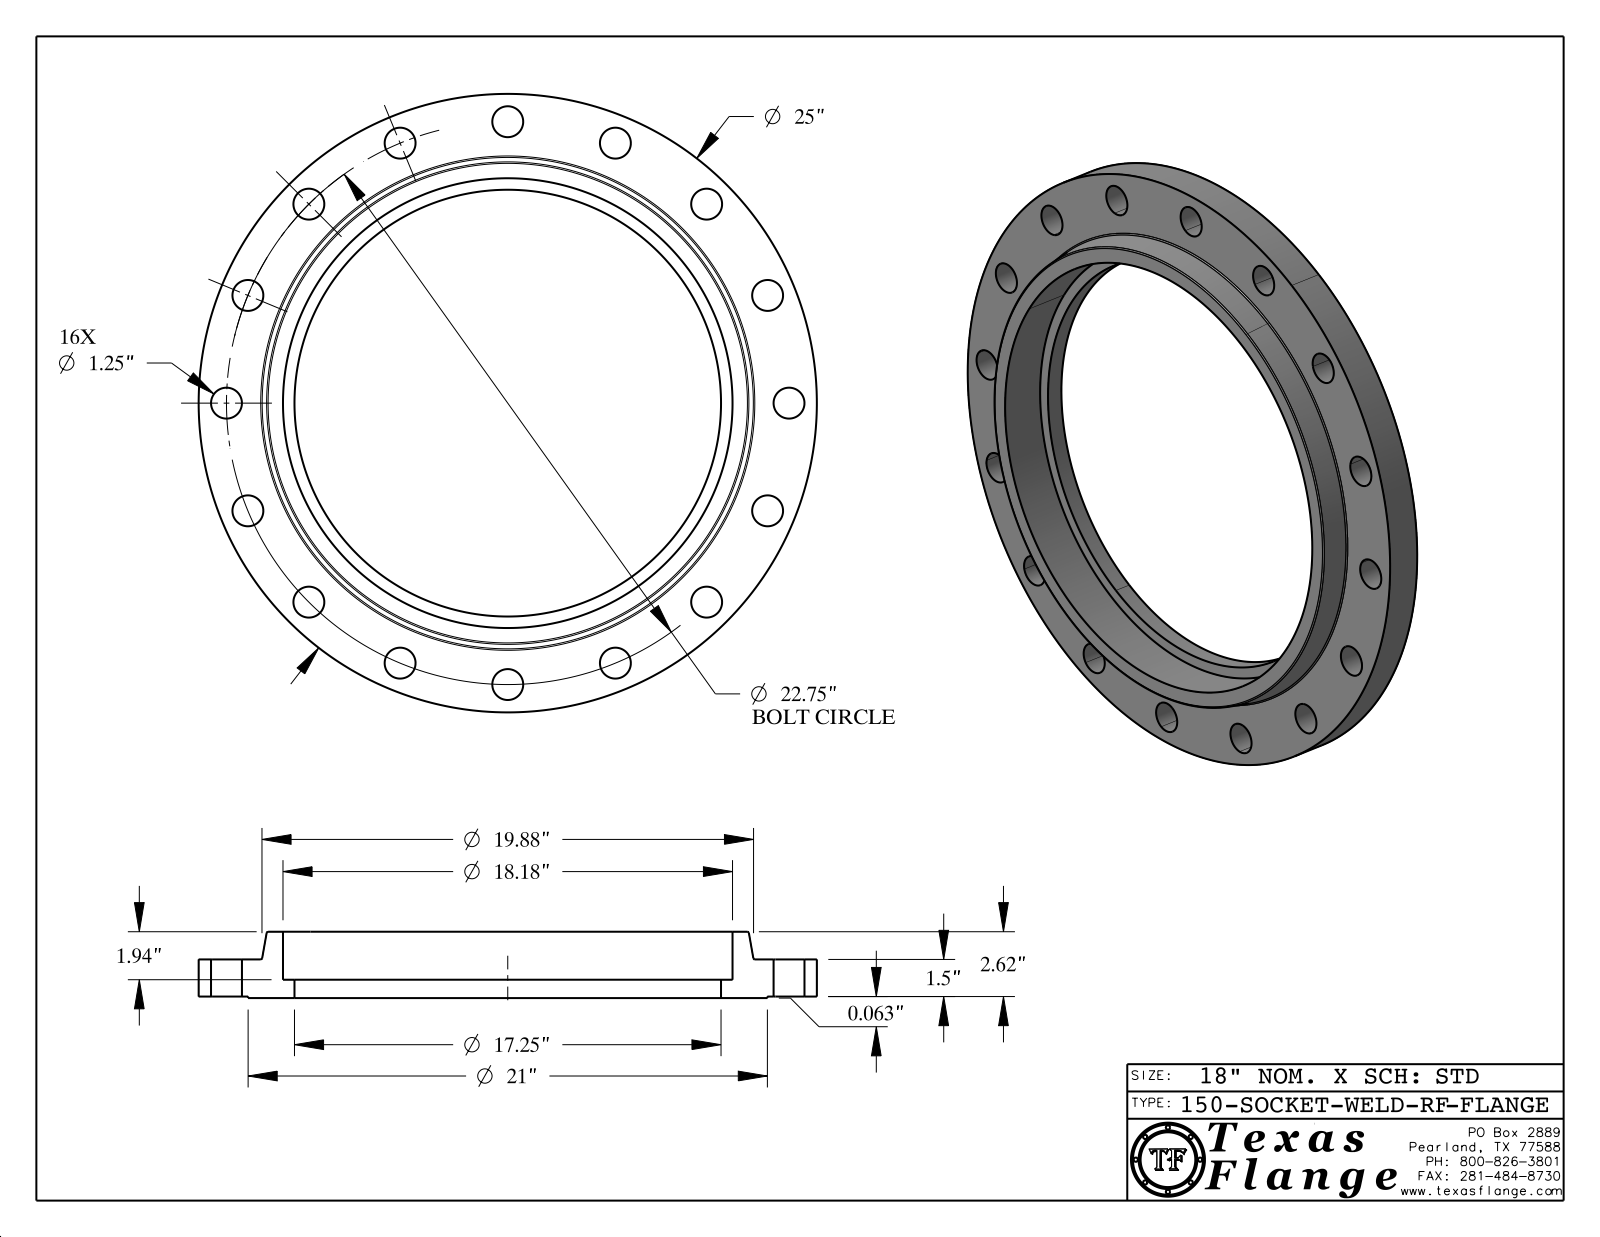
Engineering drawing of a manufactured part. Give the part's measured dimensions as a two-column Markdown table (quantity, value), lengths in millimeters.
| quantity | value |
| --- | --- |
| part name | 150-SOCKET-WELD-RF |
| STEP written by | CATIA V5 STEP AP214 (AUTOMOTIVE_DESIGN) |
| units | millimeters |
| bodies | 1 solid, 436 faces (370 planar, 60 cylindrical, 6 other) |
| overall size | 635 × 635 × 68.1 |
| volume | 6 427 000 mm³ |
| surface area | 579 600 mm² |
| round holes (diameter × count) | 31.8 × 16, 12.6 × 1, 438.2 × 1, 461.8 × 1 |
| round bosses / shafts (diameter × count) | 0.8 × 8, 635 × 1, 533.4 × 1, 9.9 × 1 |
| main face-to-face distances | 38.1, 1.6, 39.7, 68.1, 66.5, 28.4, 18.9, 17.3, 20.8, 49.3 |
| hole center spacings | 321, 566.8, 288.9, 221.1, 408.6, 533.9, 112.7, 112.8 |
